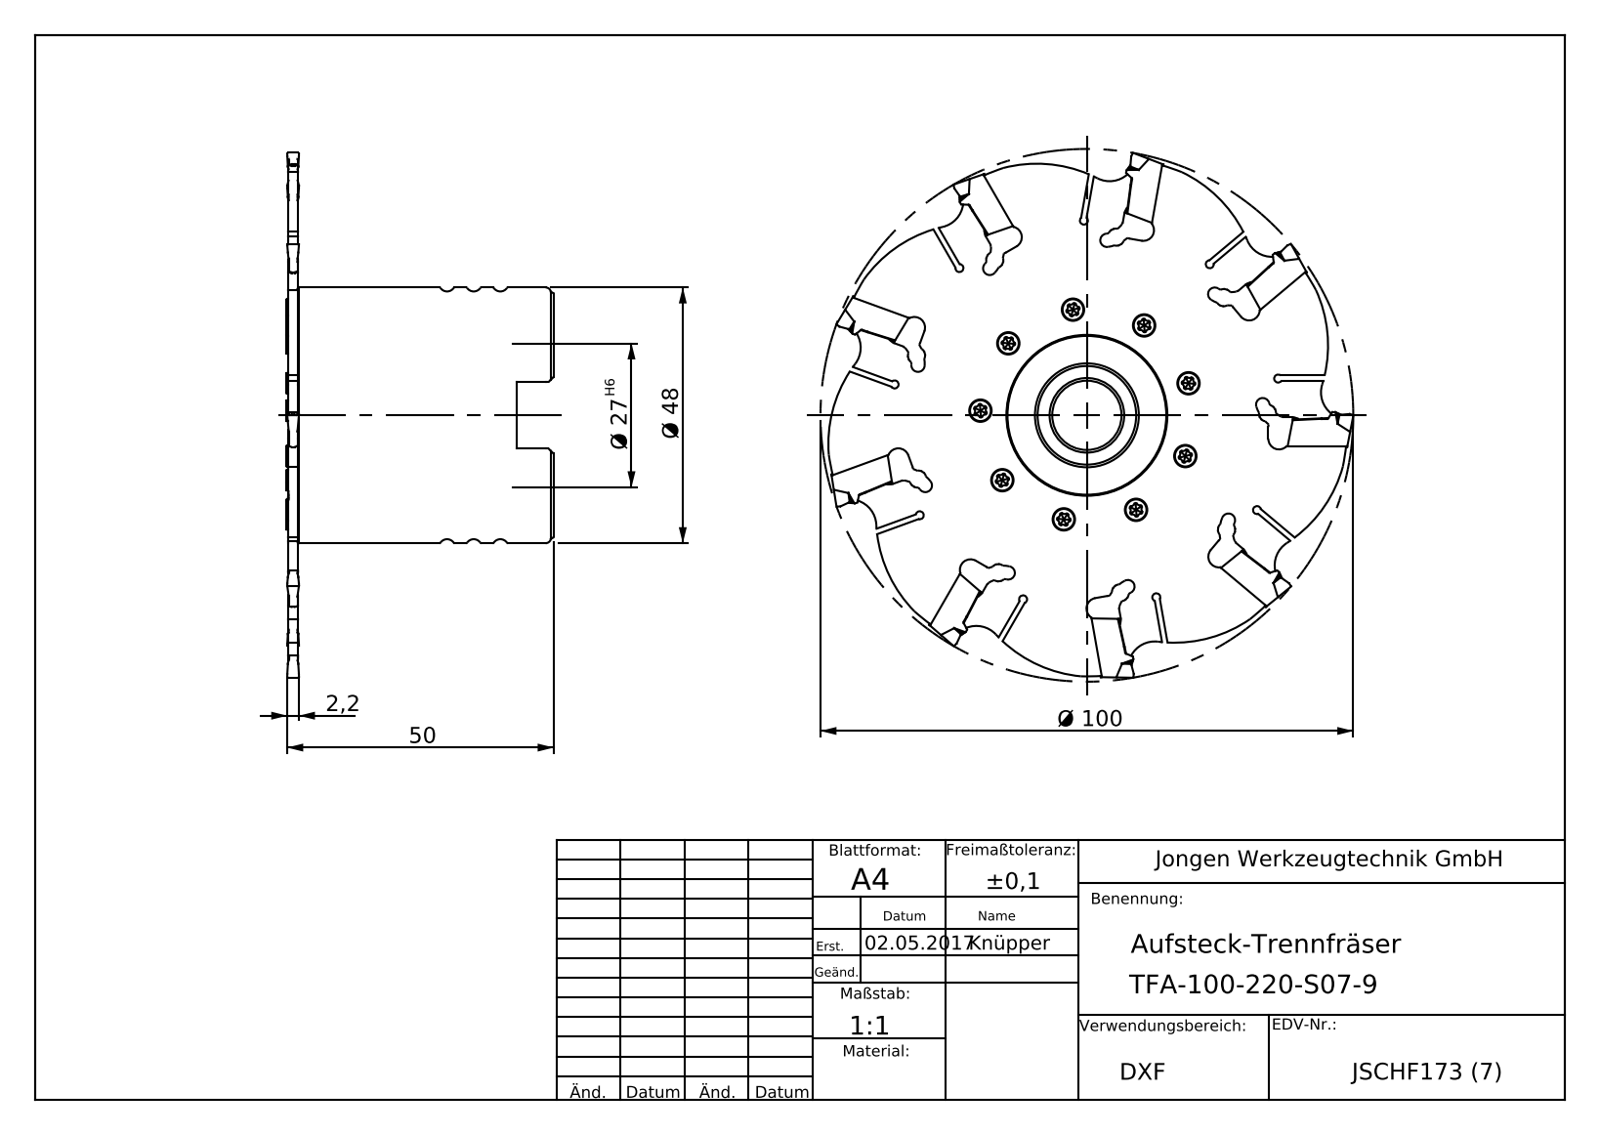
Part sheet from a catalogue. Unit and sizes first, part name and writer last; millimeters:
Units: millimetres
Overall size (bounding box): 100 × 100 × 49.8
Round holes (diameter × count): ⌀2.5 ×9, ⌀3.2 ×9, ⌀4.2 ×9, ⌀13 ×1, ⌀18.5 ×1, ⌀27 ×1, ⌀27.15 ×1, ⌀27.3 ×1, ⌀30 ×1, ⌀61.22 ×1
Round bosses / shafts (diameter × count): ⌀100 ×1, ⌀48 ×1
Main face-to-face distances: 2.2, 1.95, 1.7, 0.45, 1.5, 1.75, 47.6, 47.85, 48.05, 49.55
Hole centre spacings: 20, 25.71, 13.68, 34.64, 39.39, 39.4, 34.65, 13.69
Volume: 79 923 mm³ · Surface area: 29 917 mm²
Bodies: 2 solids, 188 faces (20 planar, 82 cylindrical, 86 other)
Part name (STEP PRODUCT): TFA-100-220-S07-9; JSCHF173 pk_Kontrolle; JSCHF173_1 pk
STEP written by: SolidWorks 2018 (AUTOMOTIVE_DESIGN)
